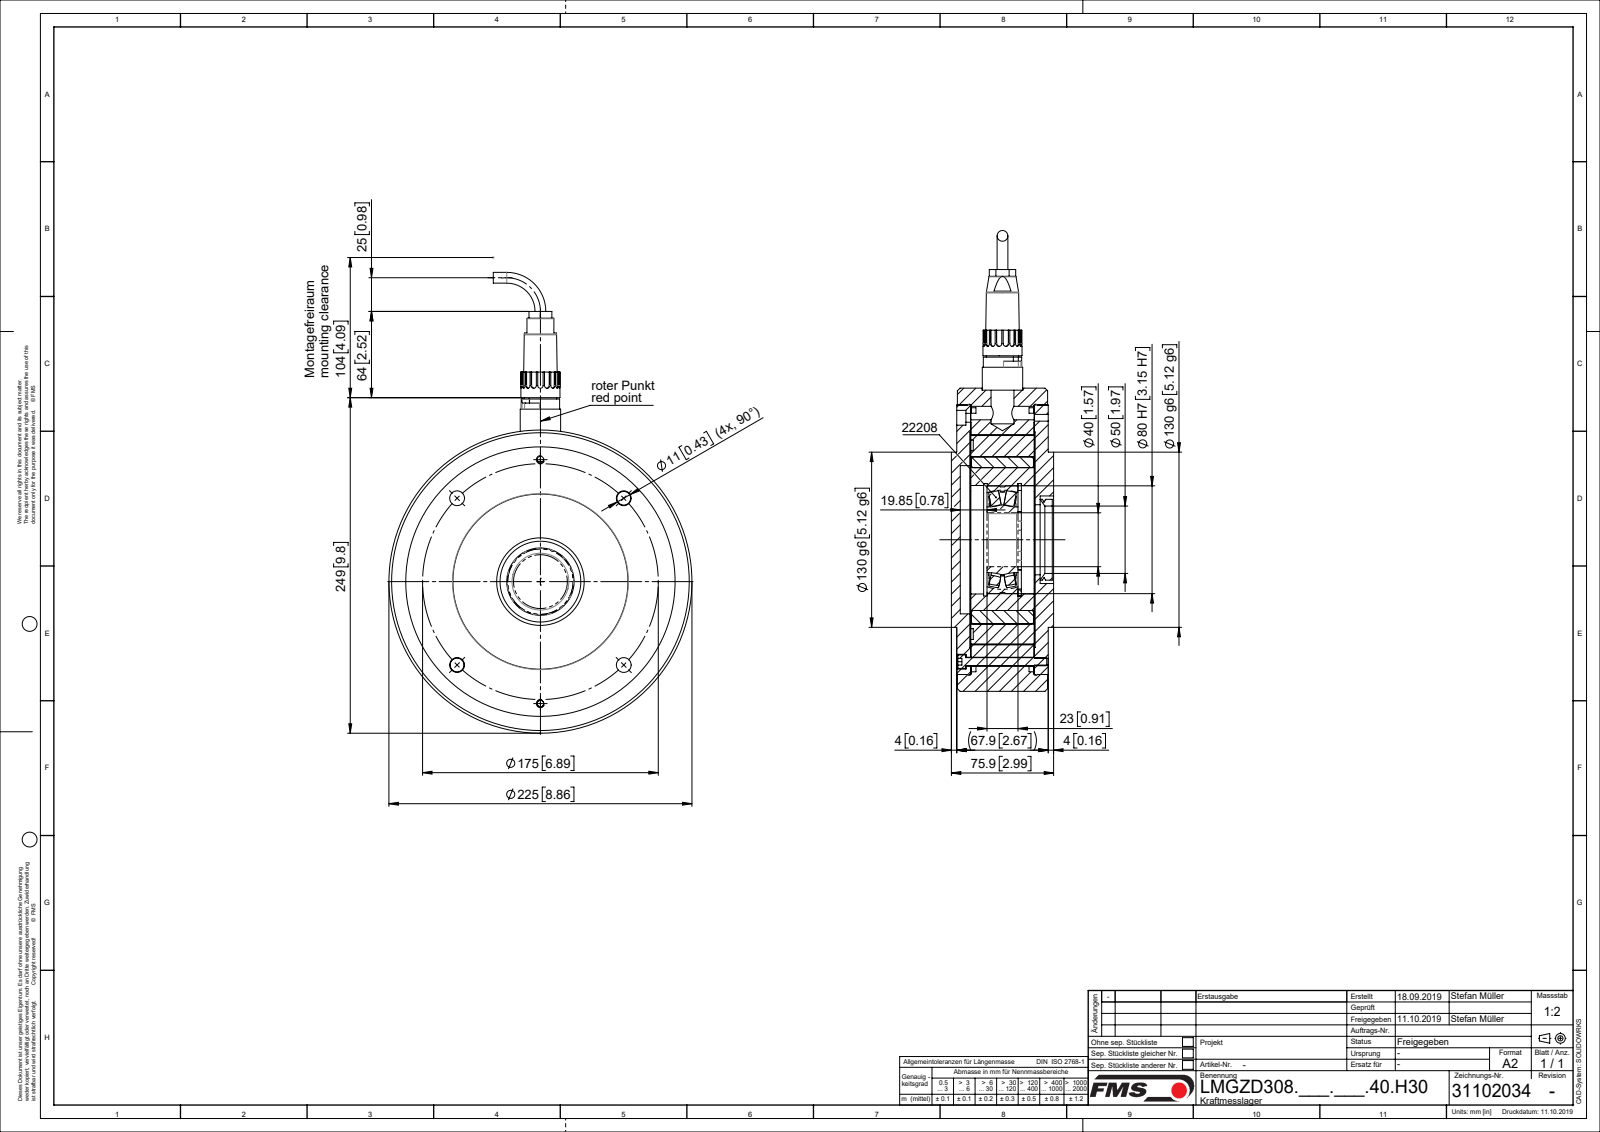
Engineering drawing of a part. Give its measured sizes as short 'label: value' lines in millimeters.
name: L50197; L4987704; TEIL1; L49531 (+8 more)
written by: Mechanical Desktop 2007 (CONFIG_CONTROL_DESIGN)
unit: mm
bodies: 17 solids, 386 faces (124 planar, 212 cylindrical, 50 other)
size: 342 × 225 × 163.32
volume: 2 548 000 mm³; area: 380 551 mm²
holes: 6× ⌀11, 4× ⌀2.49, 4× ⌀9, 2× ⌀3, 2× ⌀3.6, 2× ⌀5.15, 2× ⌀6.6, 1× ⌀10.5, 1× ⌀14, 1× ⌀22, 1× ⌀40, 1× ⌀44
bosses: 2× ⌀5.5, 1× ⌀225, 1× ⌀199, 1× ⌀130, 1× ⌀54, 1× ⌀29, 1× ⌀28.5, 1× ⌀27.5
rounds: 20× R2, 2× R3, 1× R81, 1× R86
face distances: 47.25, 47, 10.2, 10.45, 57.45, 57.7, 48, 0.5, 0.75, 47.75
hole spacings: 16.26, 23, 68.17, 87.5, 123.74, 164.45, 32.53, 90.5
